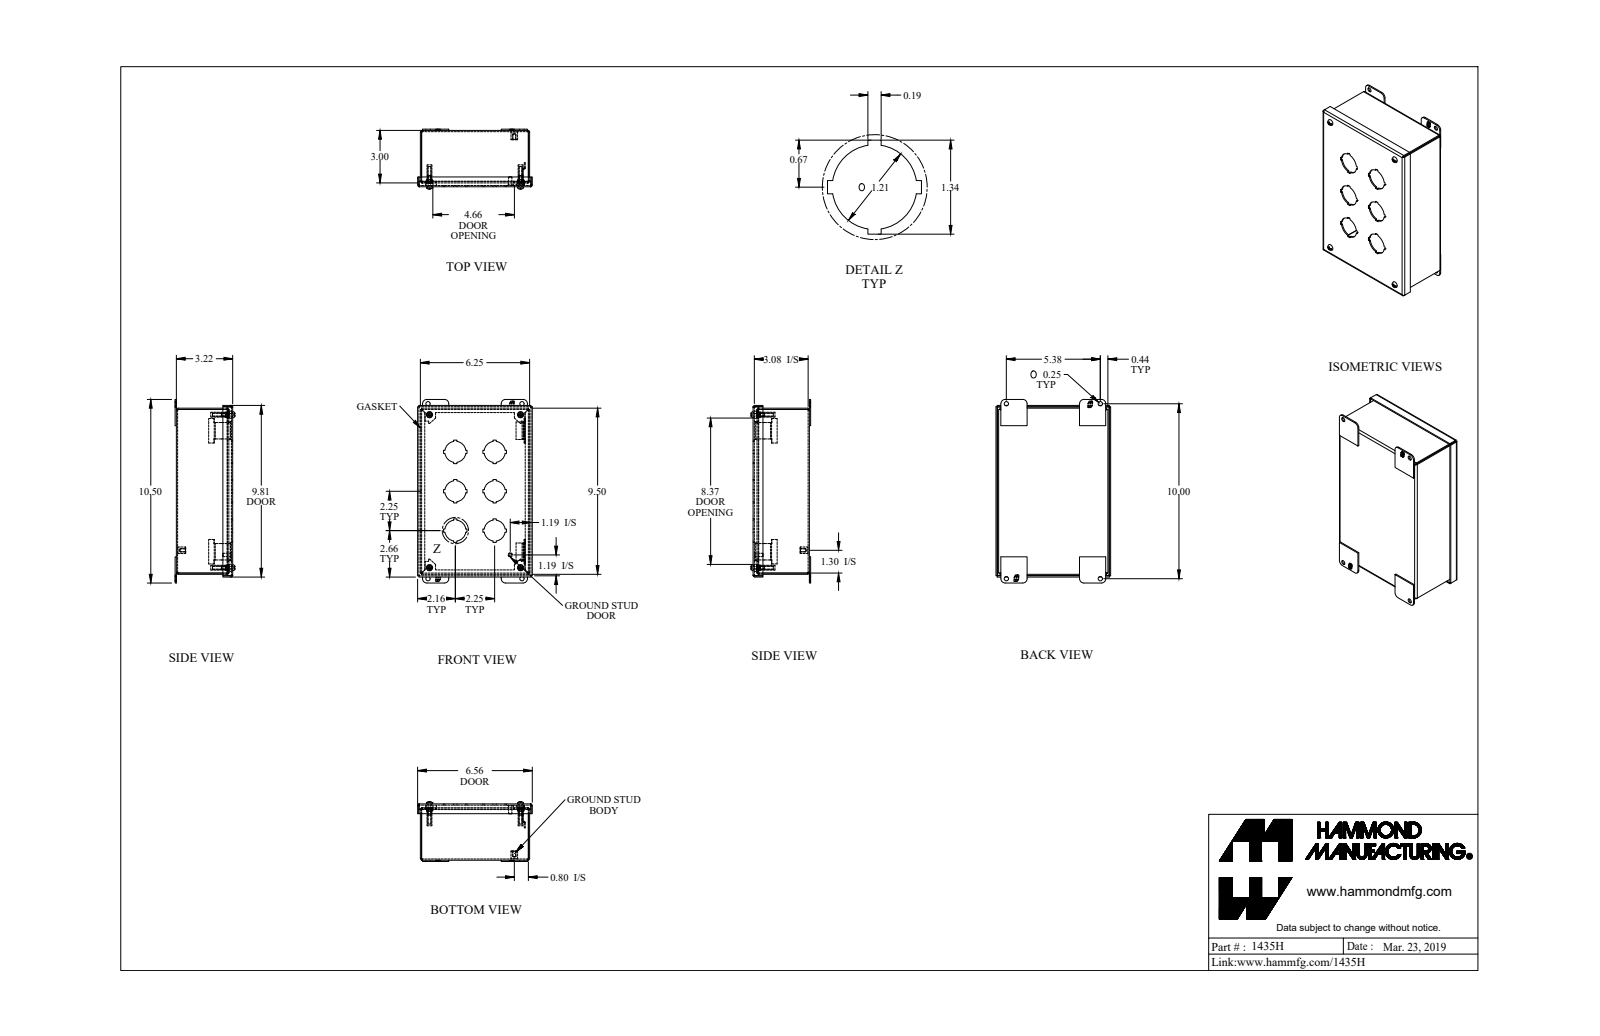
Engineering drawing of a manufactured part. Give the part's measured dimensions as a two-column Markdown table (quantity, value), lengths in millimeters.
| quantity | value |
| --- | --- |
| part name | 1435H_Default |
| STEP written by | SolidWorks 2019 (CONFIG_CONTROL_DESIGN) |
| units | millimeters |
| bodies | 23 solids, 811 faces (571 planar, 184 cylindrical, 56 other) |
| overall size | 266.7 × 166.7 × 86.9 |
| volume | 334 800 mm³ |
| surface area | 348 800 mm² |
| round holes (diameter × count) | 6.4 × 8, 30.7 × 6, 4 × 4, 10.3 × 4, 4 × 1 |
| round bosses / shafts (diameter × count) | 9.9 × 4, 7 × 4, 4.8 × 4, 3.8 × 4, 9.5 × 1, 6.4 × 1, 4.8 × 1 |
| partial cylindrical surfaces (radius × count) | 0.9 × 12, 2.7 × 12, 6.4 × 8, 0.7 × 4, 2.2 × 4, 4.1 × 4, 4.3 × 4, 3.2 × 2 |
| main face-to-face distances | 1.8, 80, 81.8, 78.2, 156.9, 239.5, 4, 158.8, 155.1, 160.9 |
| hole center spacings | 57.2, 222.3, 258.7, 117.3, 16, 65.8, 80.8, 132.3 |
